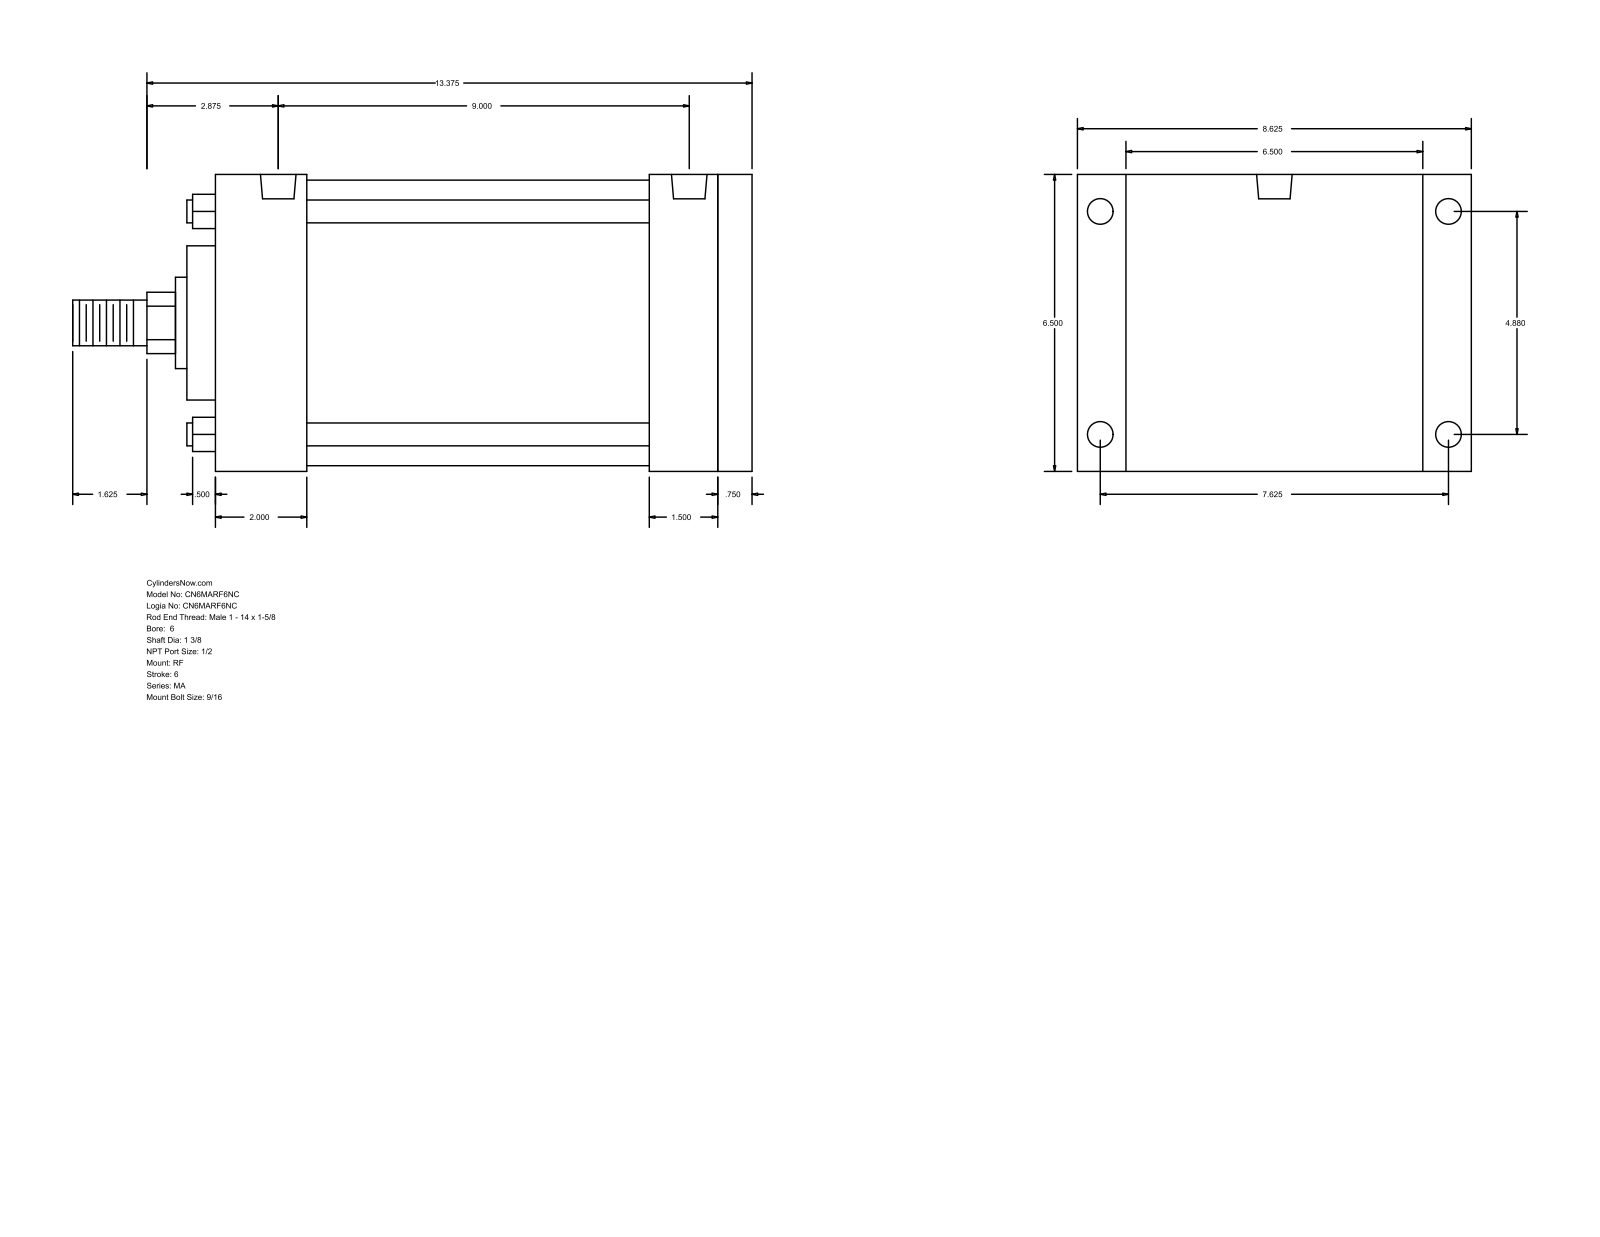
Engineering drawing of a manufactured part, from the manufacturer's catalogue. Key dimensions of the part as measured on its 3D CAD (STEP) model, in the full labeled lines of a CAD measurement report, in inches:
Part name (STEP PRODUCT): MA_RF__0600_1.375
STEP written by: GSSL Pune (CONFIG_CONTROL_DESIGN)
Units: inches
Bodies: 0 solids, 94 faces (65 planar, 29 cylindrical, 0 other)
Overall size (bounding box): 15 × 8.625 × 6.5
Round holes (diameter × count): ⌀0.563 ×4, ⌀0.687 ×4, ⌀0.778 ×2
Round bosses / shafts (diameter × count): ⌀0.5 ×4, ⌀6.25 ×1, ⌀3.375 ×1, ⌀2 ×1, ⌀1.375 ×1, ⌀1 ×1
Partial cylindrical surfaces — rounded edges, fillets, slot ends (radius × count): R0.672 ×1
Main face-to-face distances: 6.5, 11.875, 0.75, 11.125, 2, 9.125, 9.875, 9.625, 7.625, 1.5
Hole centre spacings: 4.88, 7.625, 9.053, 9.125, 0.125, 9
